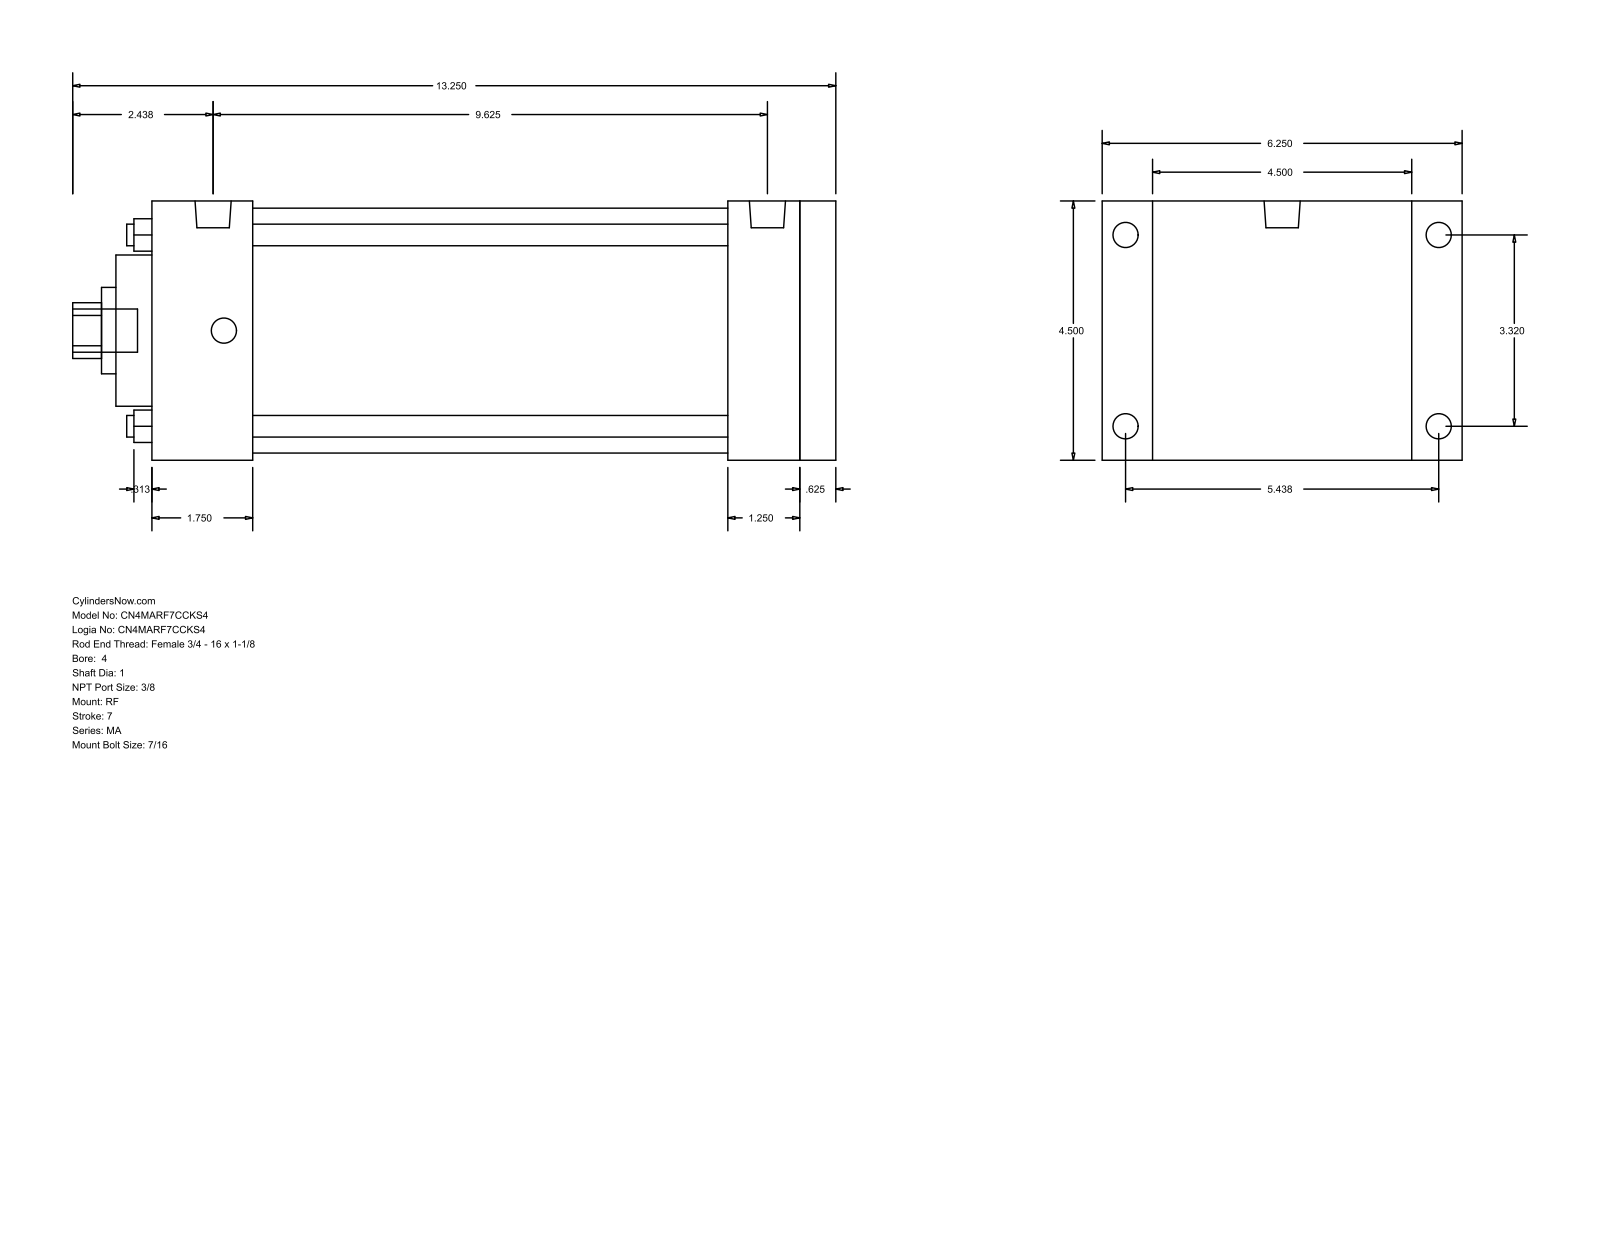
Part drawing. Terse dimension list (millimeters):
name: MA_RF__0400_1
written by: GSSL Pune (CONFIG_CONTROL_DESIGN)
unit: mm
bodies: 0 solids, 94 faces (65 planar, 29 cylindrical, 0 other)
size: 336.55 × 158.75 × 114.3
holes: 4× ⌀9.53, 1× ⌀25.4, 1× ⌀38.1, 1× ⌀66.67, 1× ⌀107.95
bosses: 8× ⌀11.11, 2× ⌀15.93, 1× ⌀19.05
rounds: 1× R12.29
face distances: 114.3, 301.63, 15.87, 285.76, 22.23, 136.53, 254.01, 31.75, 47.62, 44.46
hole spacings: 59.62, 84.32, 119.25
